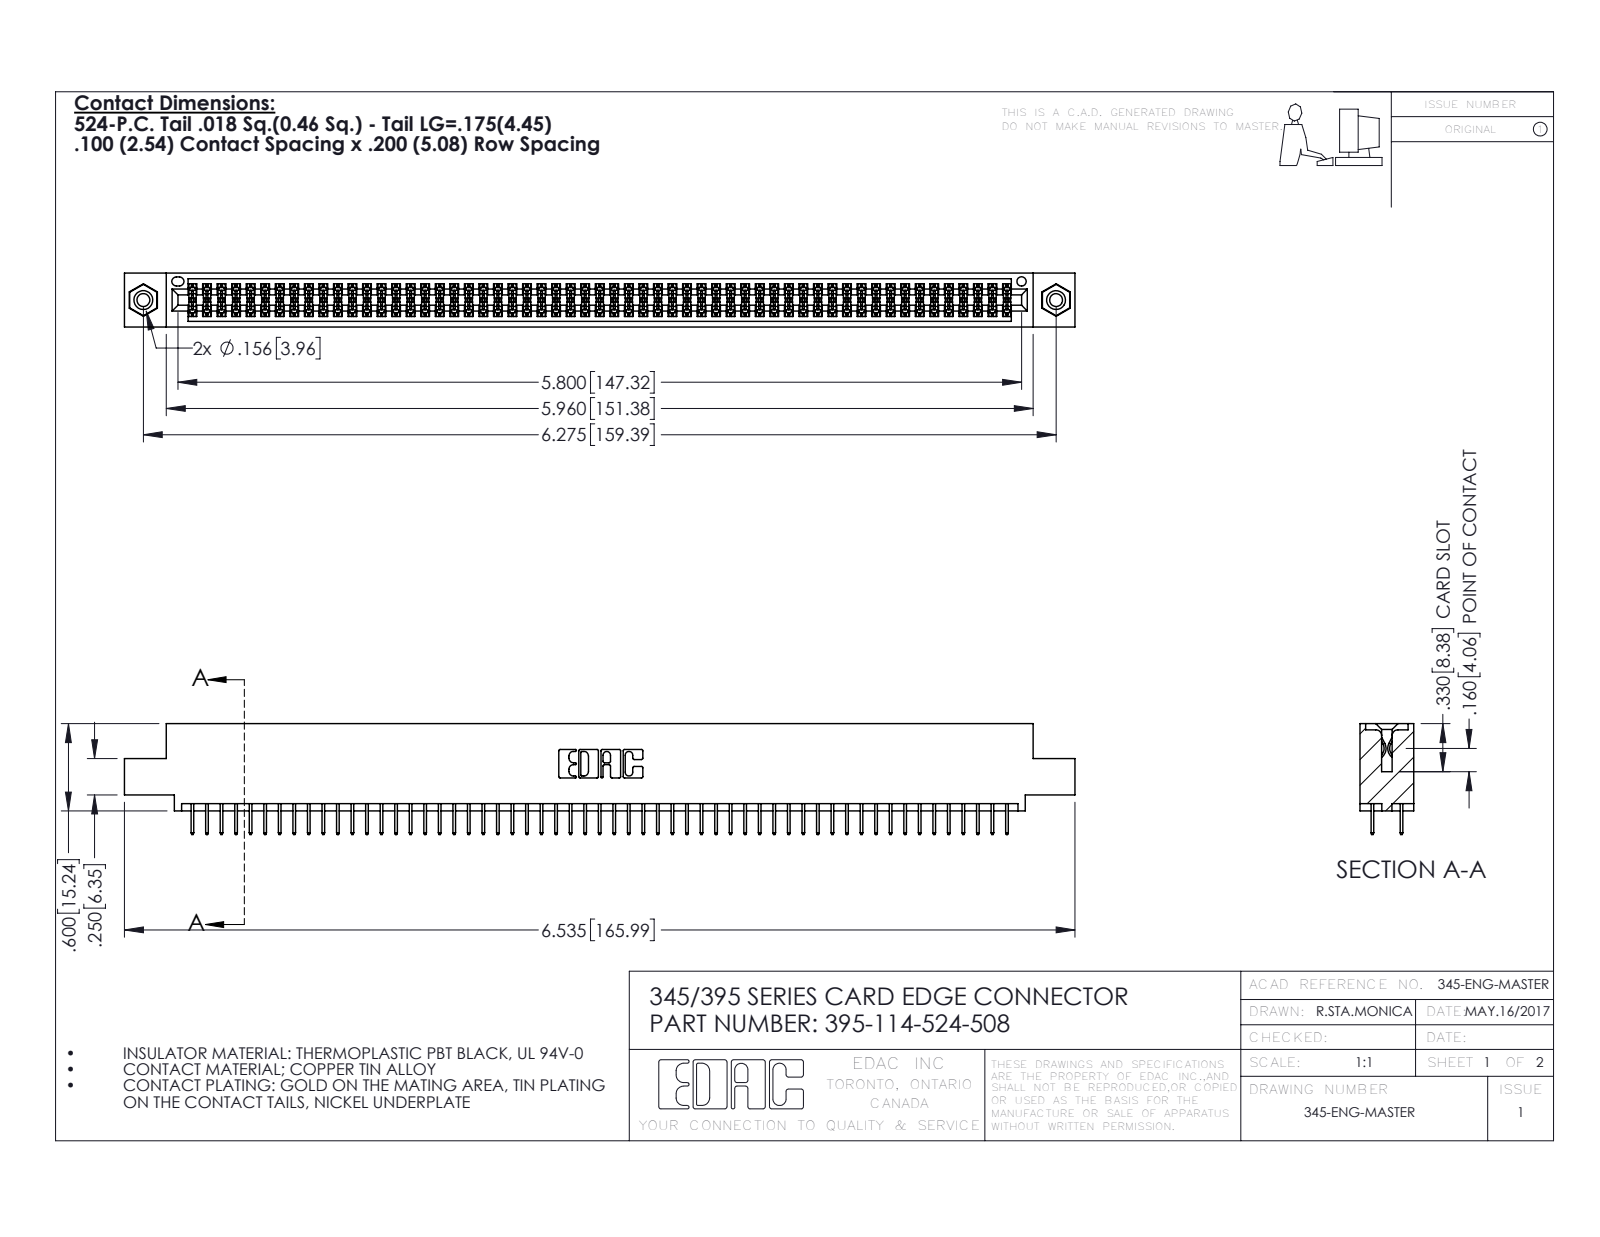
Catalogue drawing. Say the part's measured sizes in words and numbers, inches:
The part is named "345-292-001_345-293-124; 345-250-001_345-250-003-102; 395-114-524-508; 345 Part_0.110 Offset - 0.156 Dia-TI". Its 3-D file was written by "SolidWorks 2016 (CONFIG_CONTROL_DESIGN)". It is 117 solids with 6346 faces: 4562 planar, 1768 cylindrical and 16 other. Overall it measures 6.535 by 0.762 by 0.37 inches. Its volume is 0.977 cubic inches and its surface area 36.59 square inches. Round holes: 2 of diameter 0.089, 2 of diameter 0.125, 2 of diameter 0.156, 1 of diameter 0.064. Round bosses or shafts: 2 of diameter 0.155. Partial cylindrical surfaces (rounded edges, fillets, slot ends): 171 of radius 0.006, 22 of radius 0.01, 6 of radius 0.007, 6 of radius 0.031, 3 of radius 0.026, 2 of radius 0.014, 2 of radius 0.019, 2 of radius 0.022. The main face-to-face distances are 0.072, 0.298, 0.2, 0.37, 0.098, 0.272, 0.025, 0.225, 0.072, 0.175. The hole center spacings are 0.27, 6.039, 6.275.
